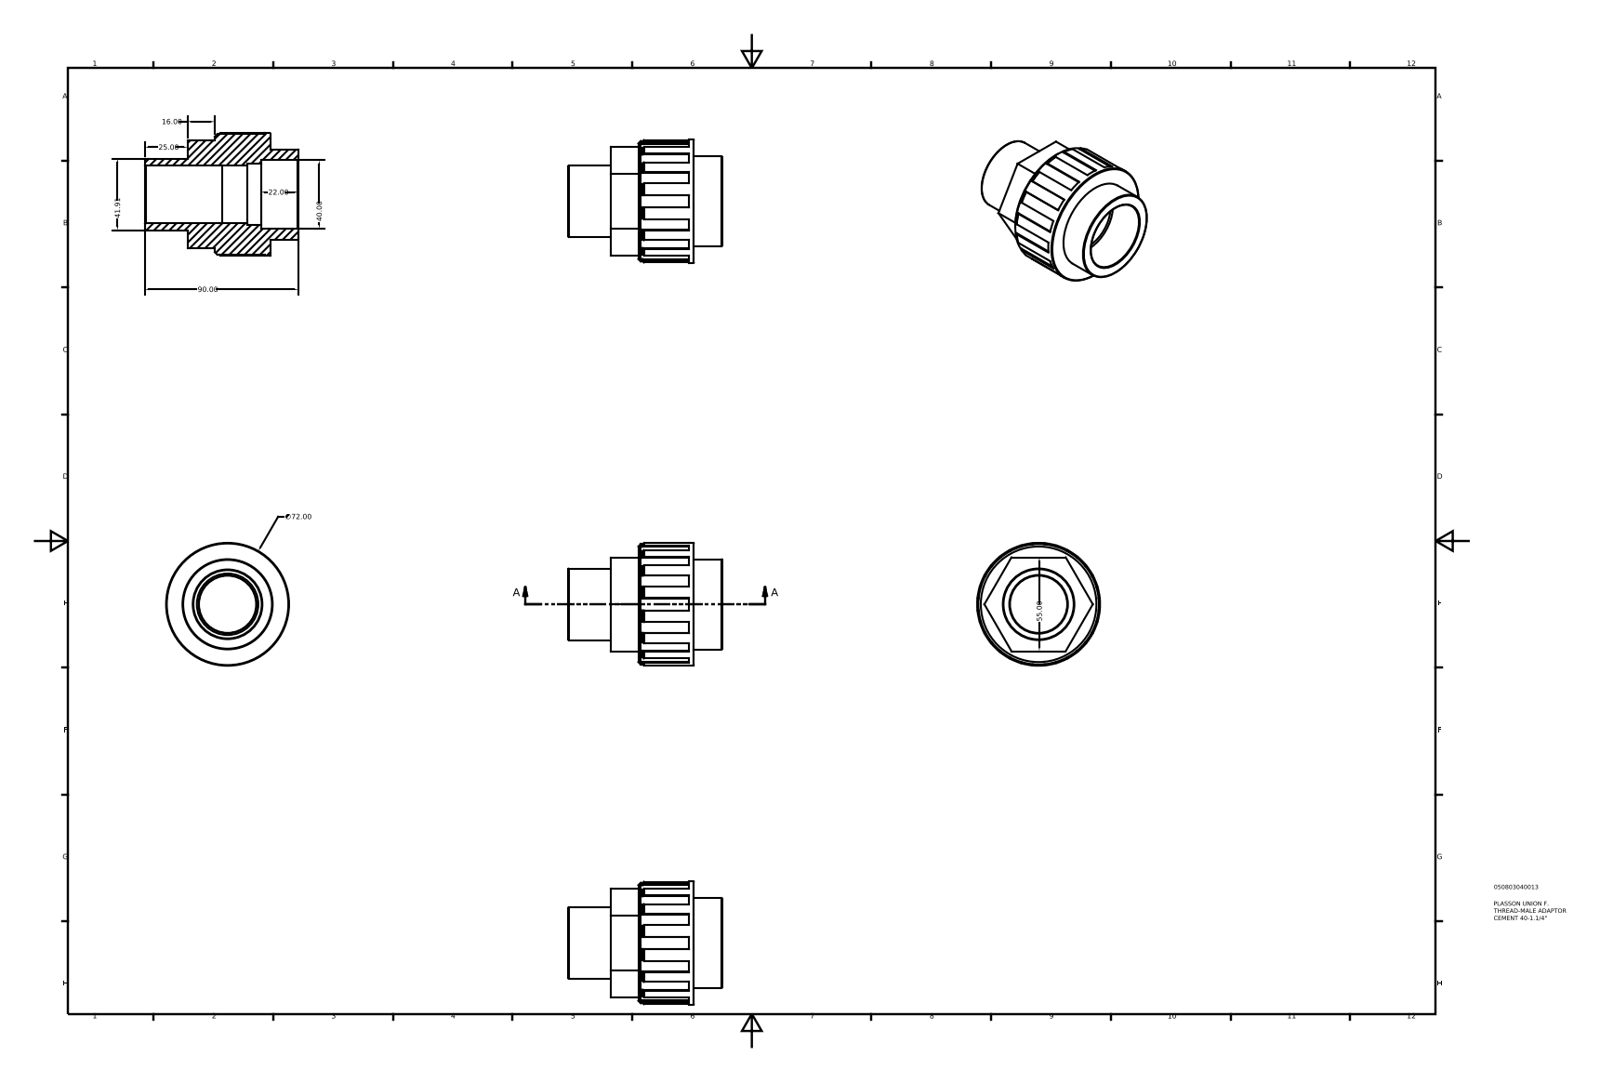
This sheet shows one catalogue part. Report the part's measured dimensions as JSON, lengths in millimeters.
{"part_name": "050803040013", "step_written_by": "Autodesk Inventor 2015 (AUTOMOTIVE_DESIGN)", "units": "millimeters", "bodies": {"solids": 1, "faces": 92, "planar": 62, "cylindrical": 8, "other": 22}, "overall_size": [90, 72, 72], "volume_mm3": 152815, "surface_area_mm2": 32991, "round_holes": [[33.53, 1], [34, 1], [36, 1], [40, 1]], "round_bosses_or_shafts": [[72, 1], [70.56, 1], [52.8, 1], [41.91, 1]], "face_to_face_distances": [55, 48.5, 16, 32.5, 65, 49, 16.5, 25, 41, 73.5]}
